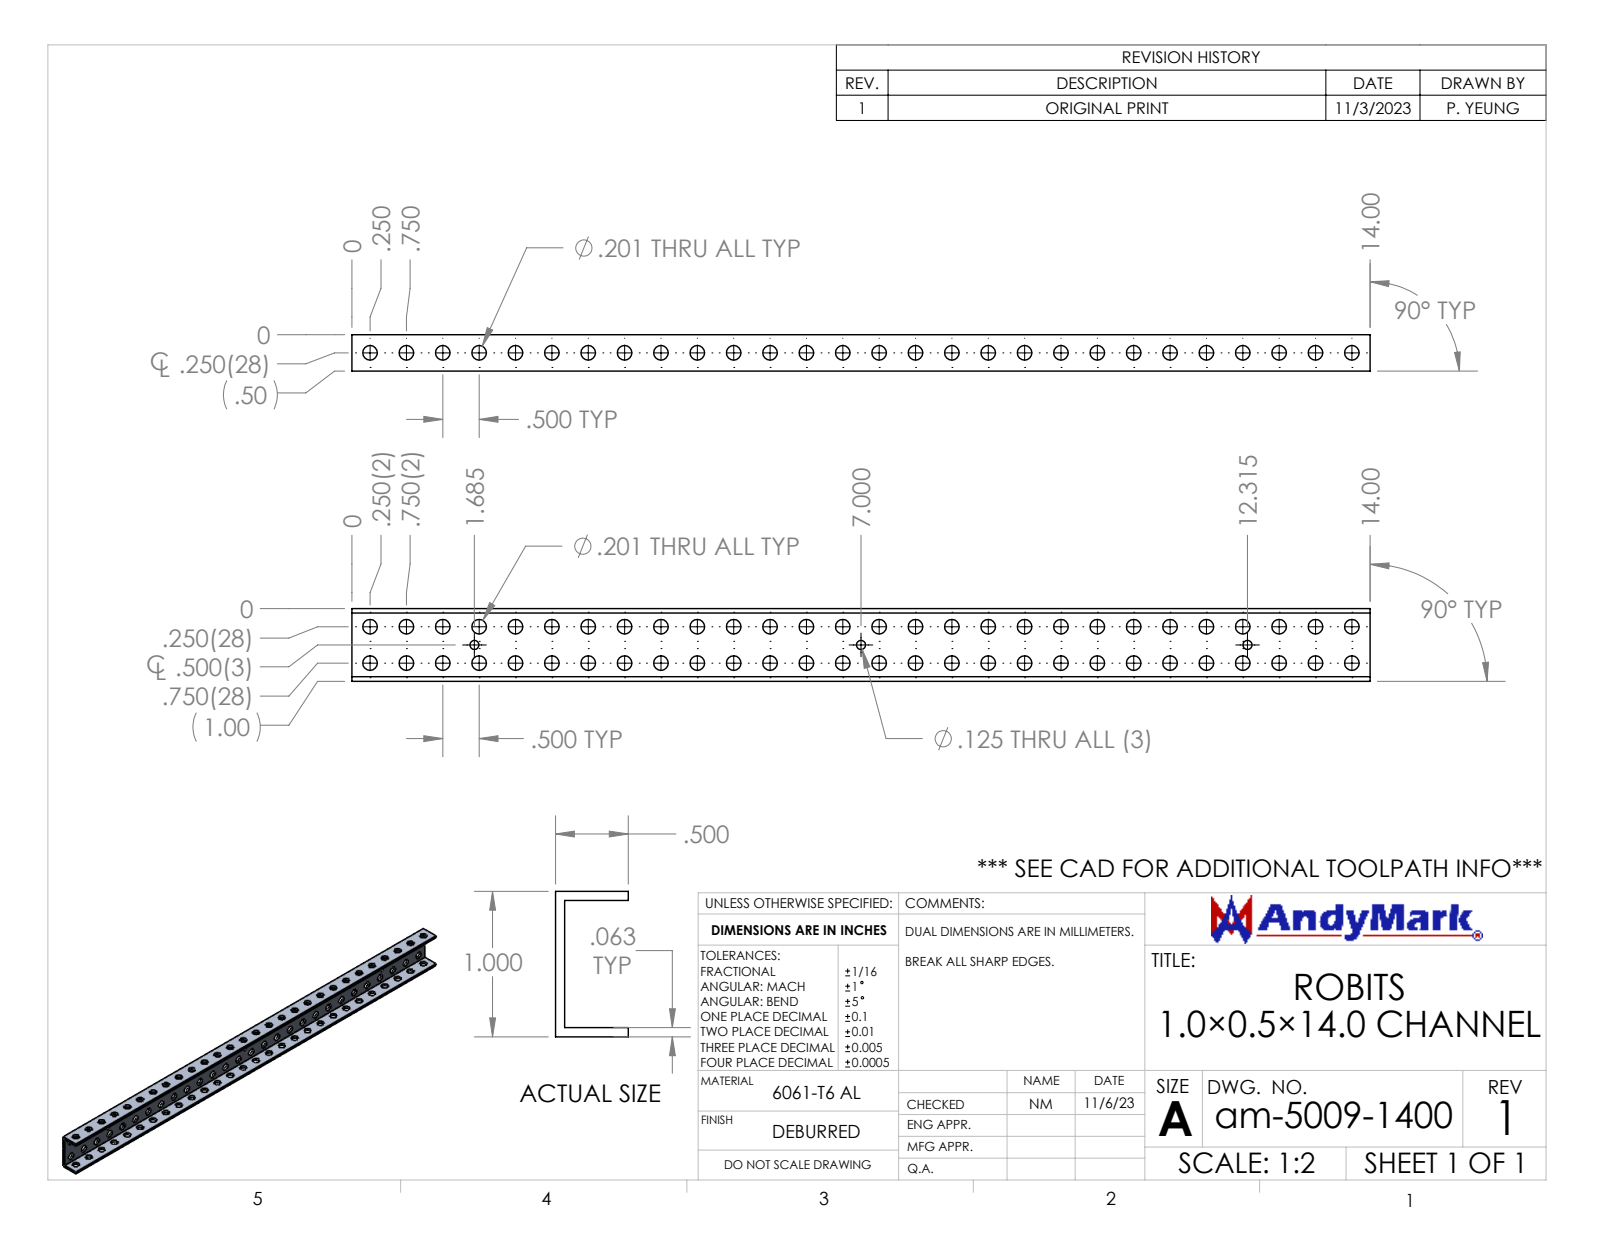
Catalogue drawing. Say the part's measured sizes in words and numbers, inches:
The part is named "am-5009-1400 Robits 1.0x0.5x14.0 Channel". Its 3-D file was written by "SolidWorks 2022 (AUTOMOTIVE_DESIGN)". It is 1 solid with 240 faces: 10 planar, 230 cylindrical and 0 other. Overall it measures 14 by 1 by 0.5 inches. Its volume is 1.427 cubic inches and its surface area 51.82 square inches. Round holes: 84 of diameter 0.201, 3 of diameter 0.125. The main face-to-face distances are 0.063, 0.937, 1, 0.874, 0.5, 0.437, 14. The hole center spacings are 0.5, 1, 1.5, 2, 2.5, 3, 3.5, 4.
